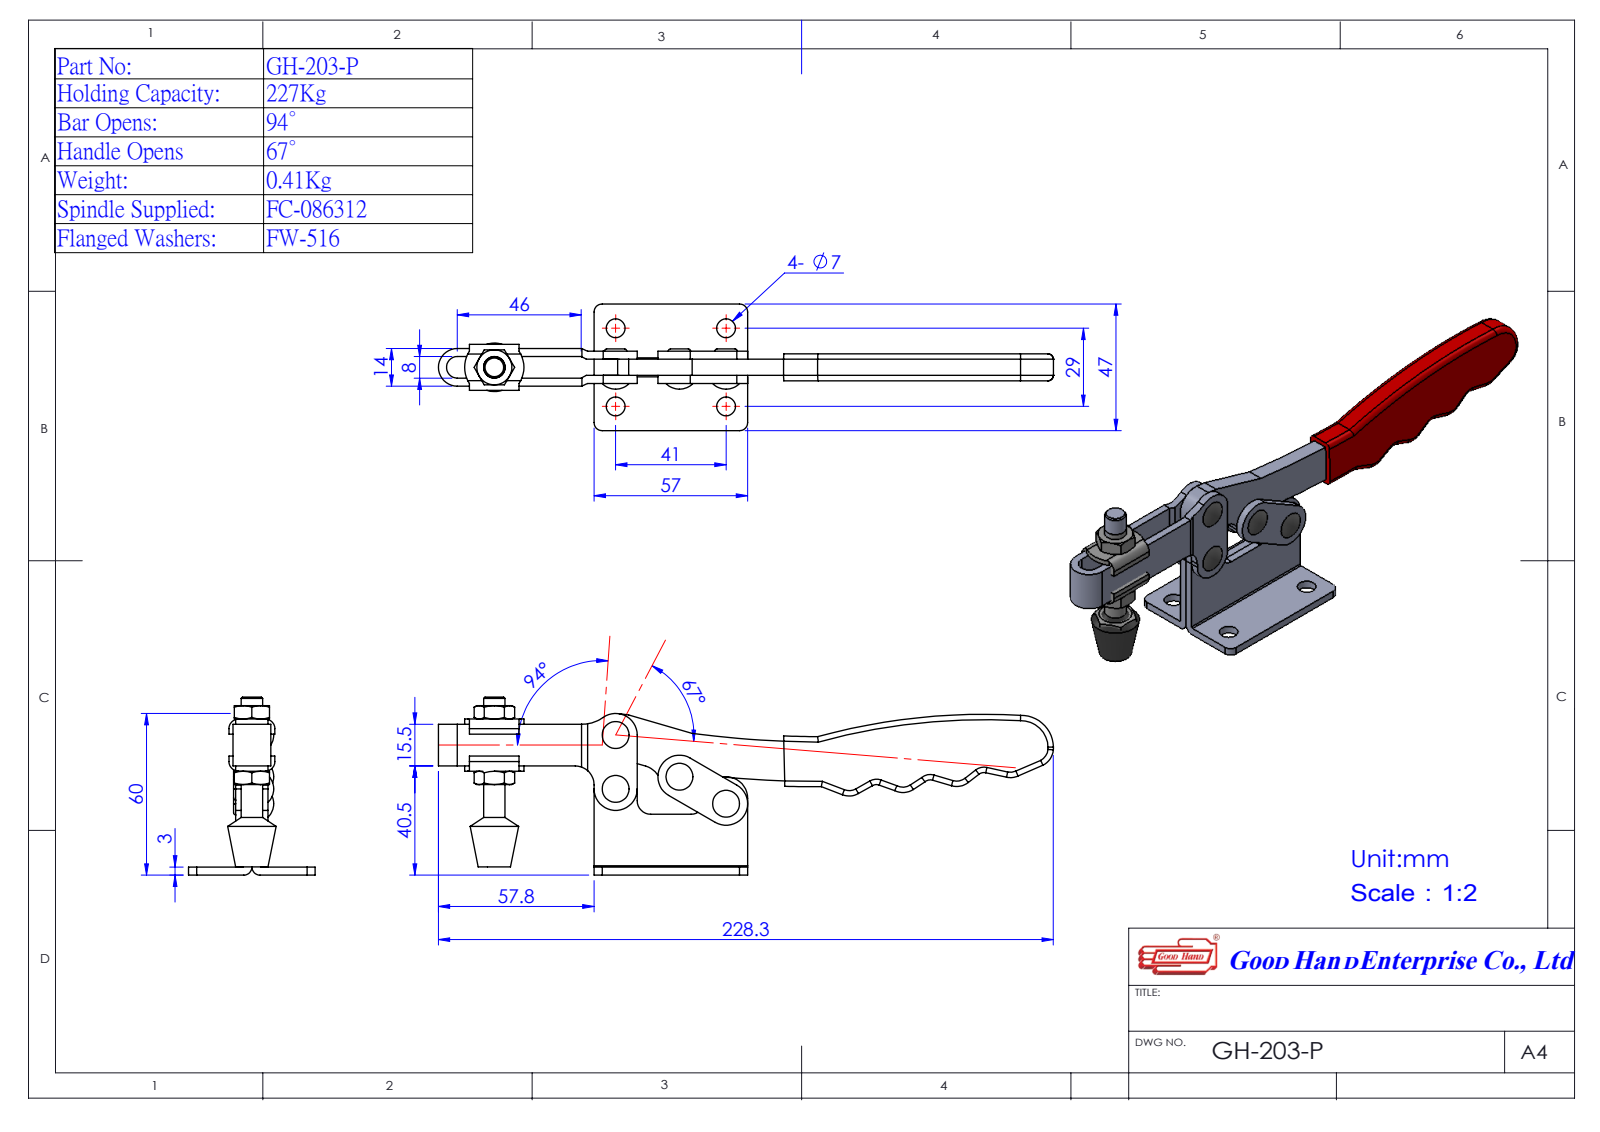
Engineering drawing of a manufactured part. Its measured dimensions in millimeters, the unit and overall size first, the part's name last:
Units: millimetres
Overall size (bounding box): 228.32 × 72 × 47
Round holes (diameter × count): ⌀5 ×4, ⌀7 ×4
Round bosses / shafts (diameter × count): ⌀6.3 ×4, ⌀16 ×1, ⌀7.93 ×1
Partial cylindrical surfaces — rounded edges, fillets, slot ends (radius × count): R8 ×6, R3 ×5, R1.5 ×4, R7 ×4, R7 ×3, R3 ×2, R5 ×2, R4 ×1
Main face-to-face distances: 2, 1, 3, 8, 10, 6, 9, 11, 12, 13
Hole centre spacings: 20, 29, 41, 50.22, 24.12, 28.3, 41.37, 48.28
Volume: 66 756 mm³ · Surface area: 34 380 mm²
Bodies: 5 solids, 271 faces (116 planar, 99 cylindrical, 56 other)
Part name (STEP PRODUCT): GH-203-P-1
STEP written by: SolidWorks 2016 (AUTOMOTIVE_DESIGN)
